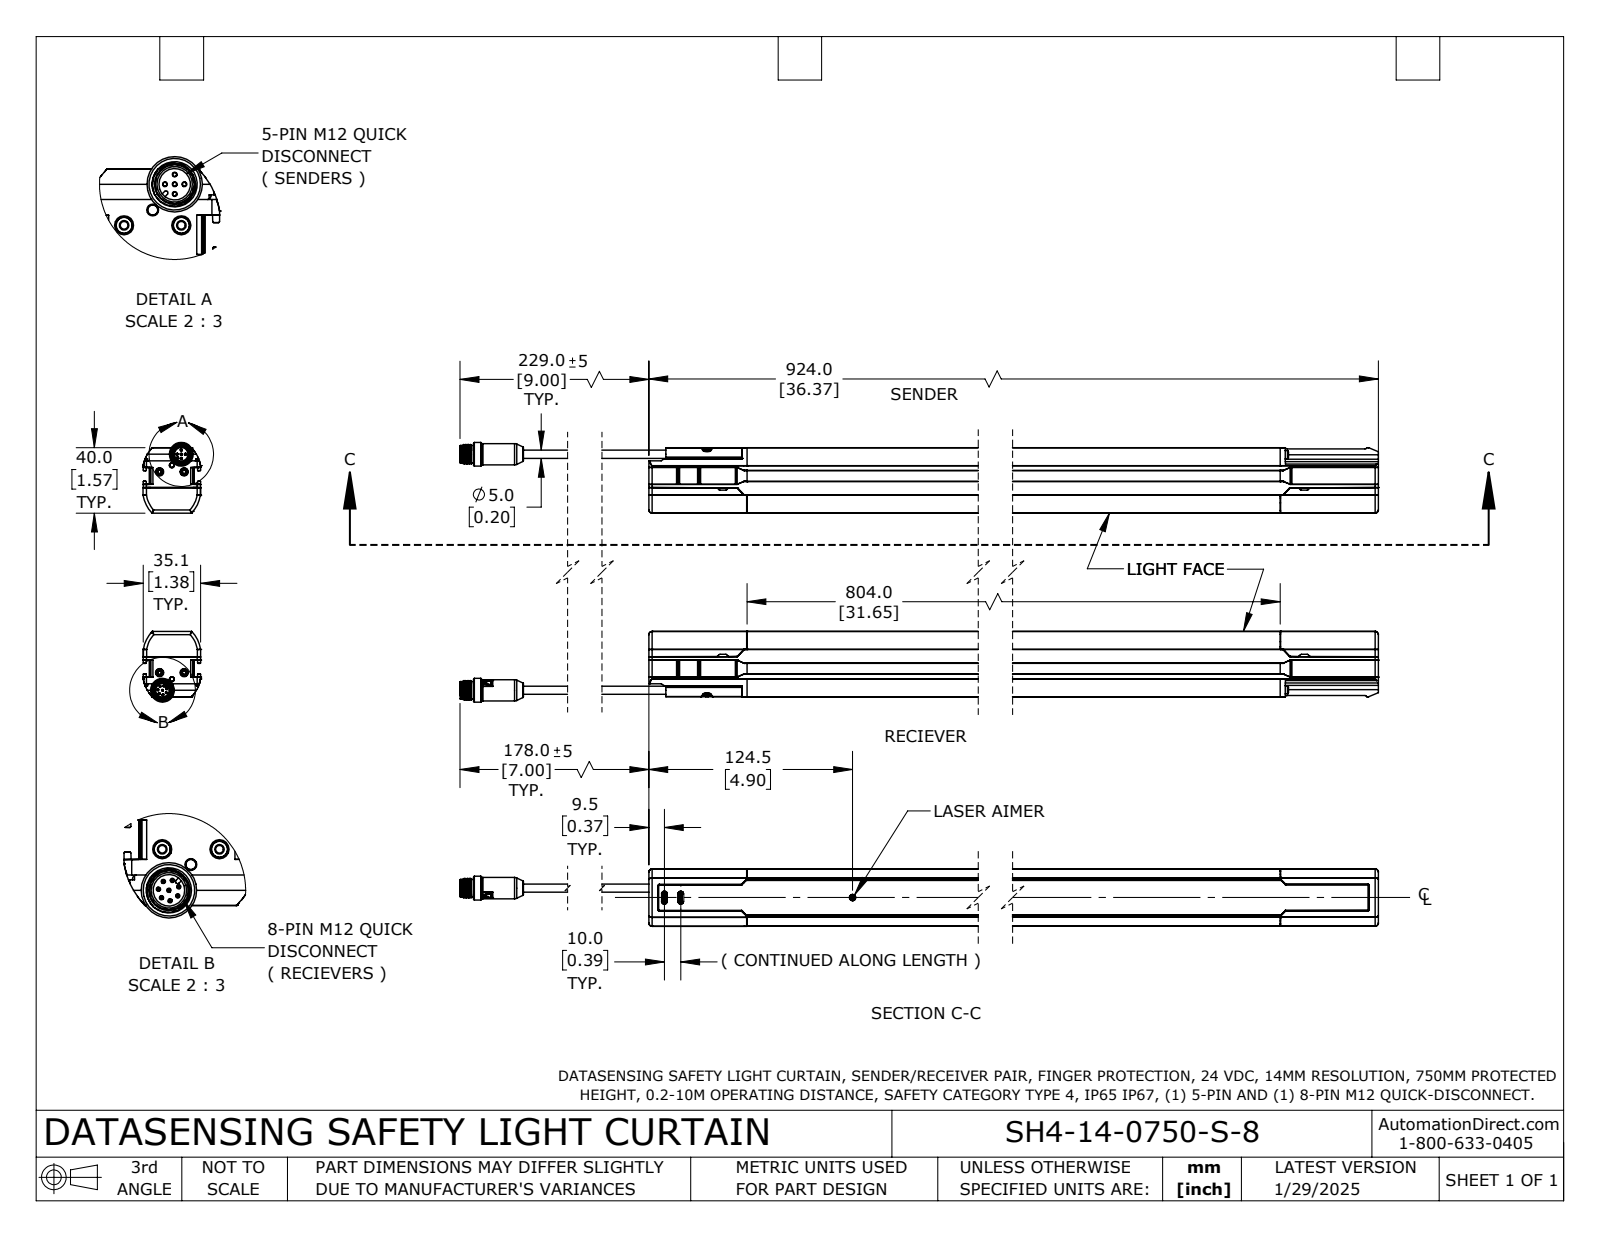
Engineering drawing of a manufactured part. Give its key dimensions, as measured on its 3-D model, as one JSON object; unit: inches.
{"part_name": "957920060", "step_written_by": "SolidWorks 2024 (AUTOMOTIVE_DESIGN)", "units": "inches", "bodies": {"solids": 4, "faces": 2616, "planar": 1194, "cylindrical": 784, "other": 638}, "overall_size": [38.87, 6.248, 1.384], "volume_in3": 108.5, "surface_area_in2": 511.2, "round_holes": [[0.079, 4], [0.118, 4], [0.197, 4], [0.1, 2], [0.101, 2], [0.101, 2], [0.101, 2], [0.325, 2], [0.382, 2], [0.407, 2], [0.425, 2], [0.11, 1]], "round_bosses_or_shafts": [[0.197, 10], [0.087, 8], [0.031, 8], [0.039, 5], [0.172, 4], [0.571, 2], [0.512, 2], [0.417, 2]], "partial_cylinders_radius": [[0.01, 164], [0.016, 66], [0.02, 50], [0.008, 36], [0.031, 20], [0.031, 12], [0.079, 12], [0.059, 10]], "face_to_face_distances": [1.496, 4.496, 0.156, 1.222, 3, 1.378, 5.992, 1.067, 1.033, 4.634], "hole_center_spacings": [0.866, 5.429, 5.497, 0.429, 0.591, 0.672, 4.831, 4.867]}
